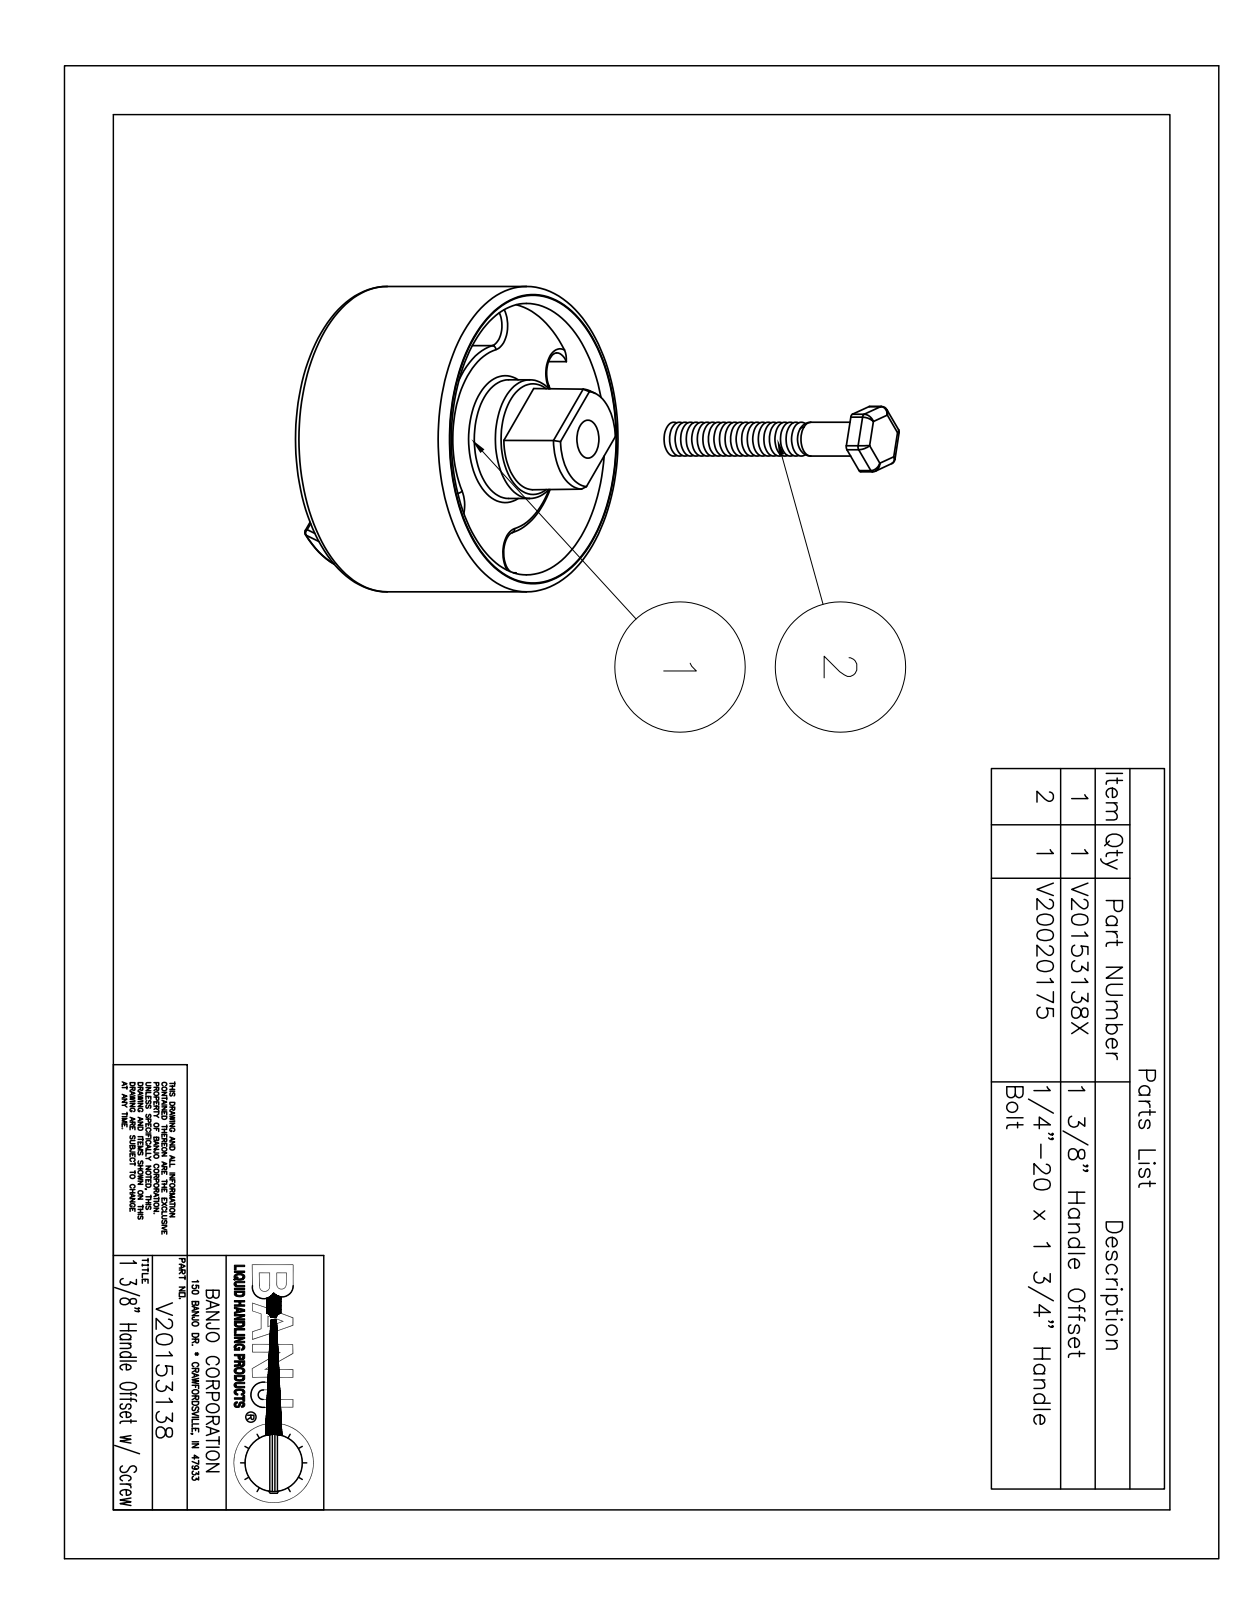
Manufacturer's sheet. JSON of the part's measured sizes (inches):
{"part_name": "V20153138; V20153138X; V20020175", "step_written_by": "Mechanical Desktop 2009 (CONFIG_CONTROL_DESIGN)", "units": "inches", "bodies": {"solids": 2, "faces": 212, "planar": 28, "cylindrical": 40, "other": 144}, "overall_size": [4.756, 2.25, 2.25], "volume_in3": 3.58, "surface_area_in2": 33.13, "round_holes": [[0.28, 1], [2, 1]], "round_bosses_or_shafts": [[2.25, 1], [0.875, 1], [0.25, 1]], "partial_cylinders_radius": [[0.03, 14], [0.06, 6], [0.15, 4], [0.38, 1], [0.7, 1], [0.78, 1]], "face_to_face_distances": [1.125, 0.5, 0.625, 0.51, 1.87, 1.37, 0.745, 1.375, 0.875, 0.25]}
